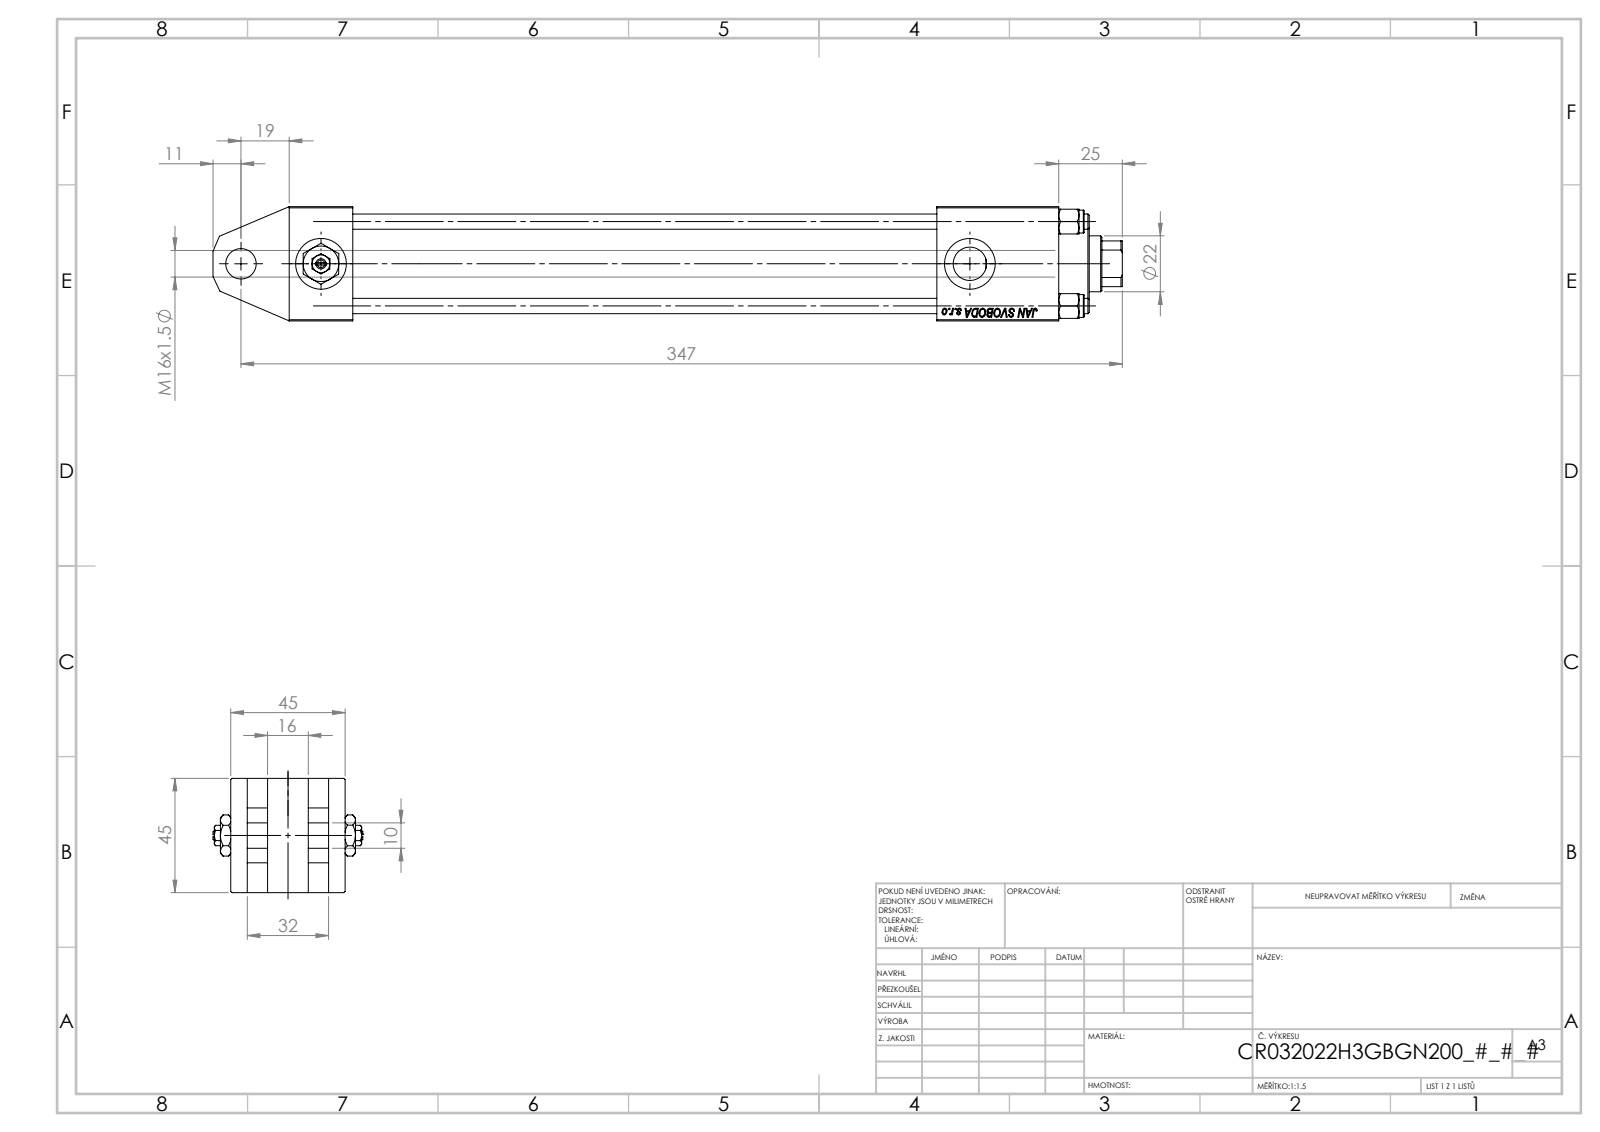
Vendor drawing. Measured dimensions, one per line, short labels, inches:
name: V215_VC_A; V215CR_TYCINKA_H; V215CR_H_Body; Zatka_pro_OIL_PORT (+2 more)
written by: SolidWorks 2019 (CONFIG_CONTROL_DESIGN)
unit: in
bodies: 13 solids, 1236 faces (564 planar, 98 cylindrical, 574 other)
size: 14.094 × 2.323 × 1.772
volume: 22.66 in³; area: 226.3 in²
holes: 4× ⌀0.236, 2× ⌀0.098, 2× ⌀0.276, 2× ⌀0.518, 2× ⌀0.787, 1× ⌀0.413, 1× ⌀0.472, 1× ⌀0.866, 1× ⌀0.945, 1× ⌀0.984, 1× ⌀1.26, 1× ⌀1.299
bosses: 4× ⌀0.354, 1× ⌀1.496, 1× ⌀1.339
rounds: 1× R0.413
face distances: 1.772, 0.315, 0.256, 1.516, 0.571, 1.201, 0.945, 0.984, 11.929, 10.039
hole spacings: 0.657, 0.924, 1.307, 1.396, 0.581, 1.848, 1.161, 1.24
